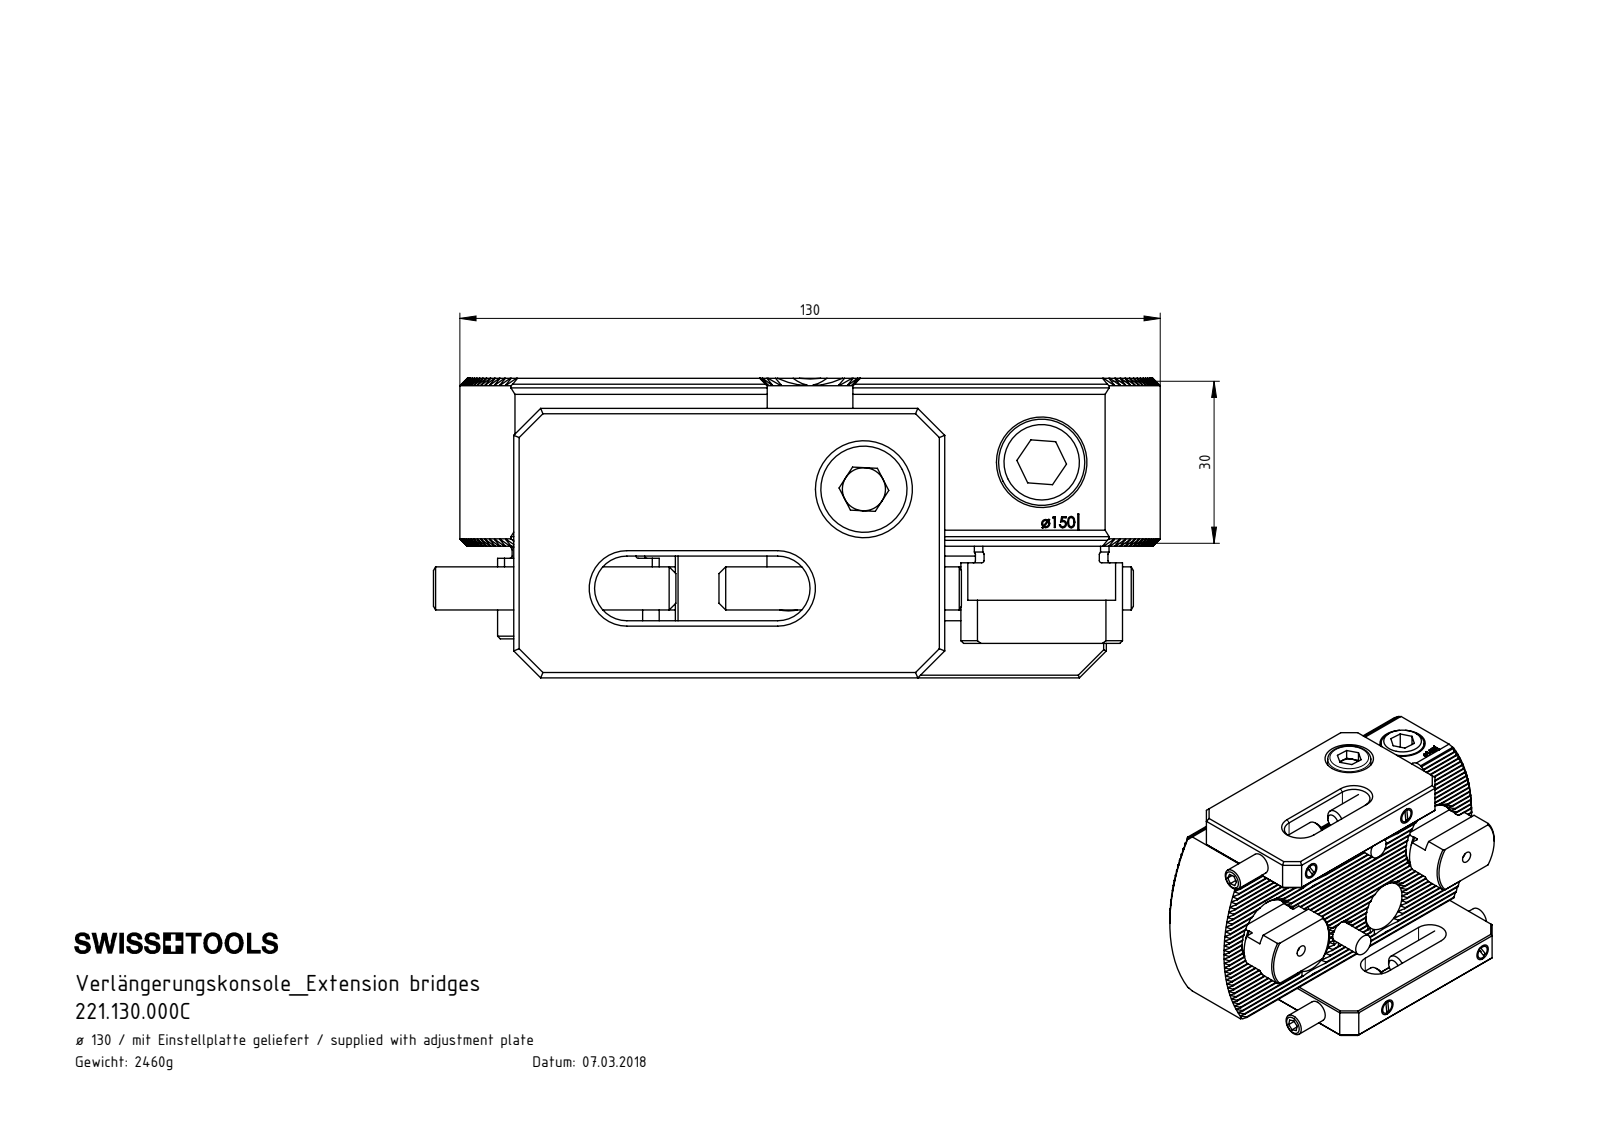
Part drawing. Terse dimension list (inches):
name: 221.130.000C; VK1-ER3.001.028_A_PreviewCfg; VK1-ER7.001.012_mit kurzer Schraube; VK1-ER1.001.030_A (+8 more)
written by: SolidWorks 2017 (CONFIG_CONTROL_DESIGN)
unit: in
bodies: 27 solids, 1743 faces (968 planar, 467 cylindrical, 308 other)
size: 5.118 × 3.74 × 2.188
volume: 19.52 in³; area: 156.9 in²
holes: 4× ⌀0.197, 4× ⌀0.236, 4× ⌀0.268, 4× ⌀0.512, 4× ⌀0.748, 2× ⌀0.079, 2× ⌀0.315, 2× ⌀0.335, 2× ⌀0.413, 2× ⌀0.433, 2× ⌀0.551, 2× ⌀0.709
bosses: 4× ⌀0.63, 4× ⌀0.236, 2× ⌀0.394, 2× ⌀0.315
rounds: 66× R0.006, 8× R0.079, 4× R0.236, 2× R0.484, 2× R0.591, 1× R0.313, 1× R2.559
face distances: 0.472, 3.228, 2.756, 0.02, 3.248, 0.453, 0.068, 2.776, 3.701, 2.795
hole spacings: 1.23, 2.565, 3.386, 0.081, 0.263, 0.311, 0.591, 0.669
